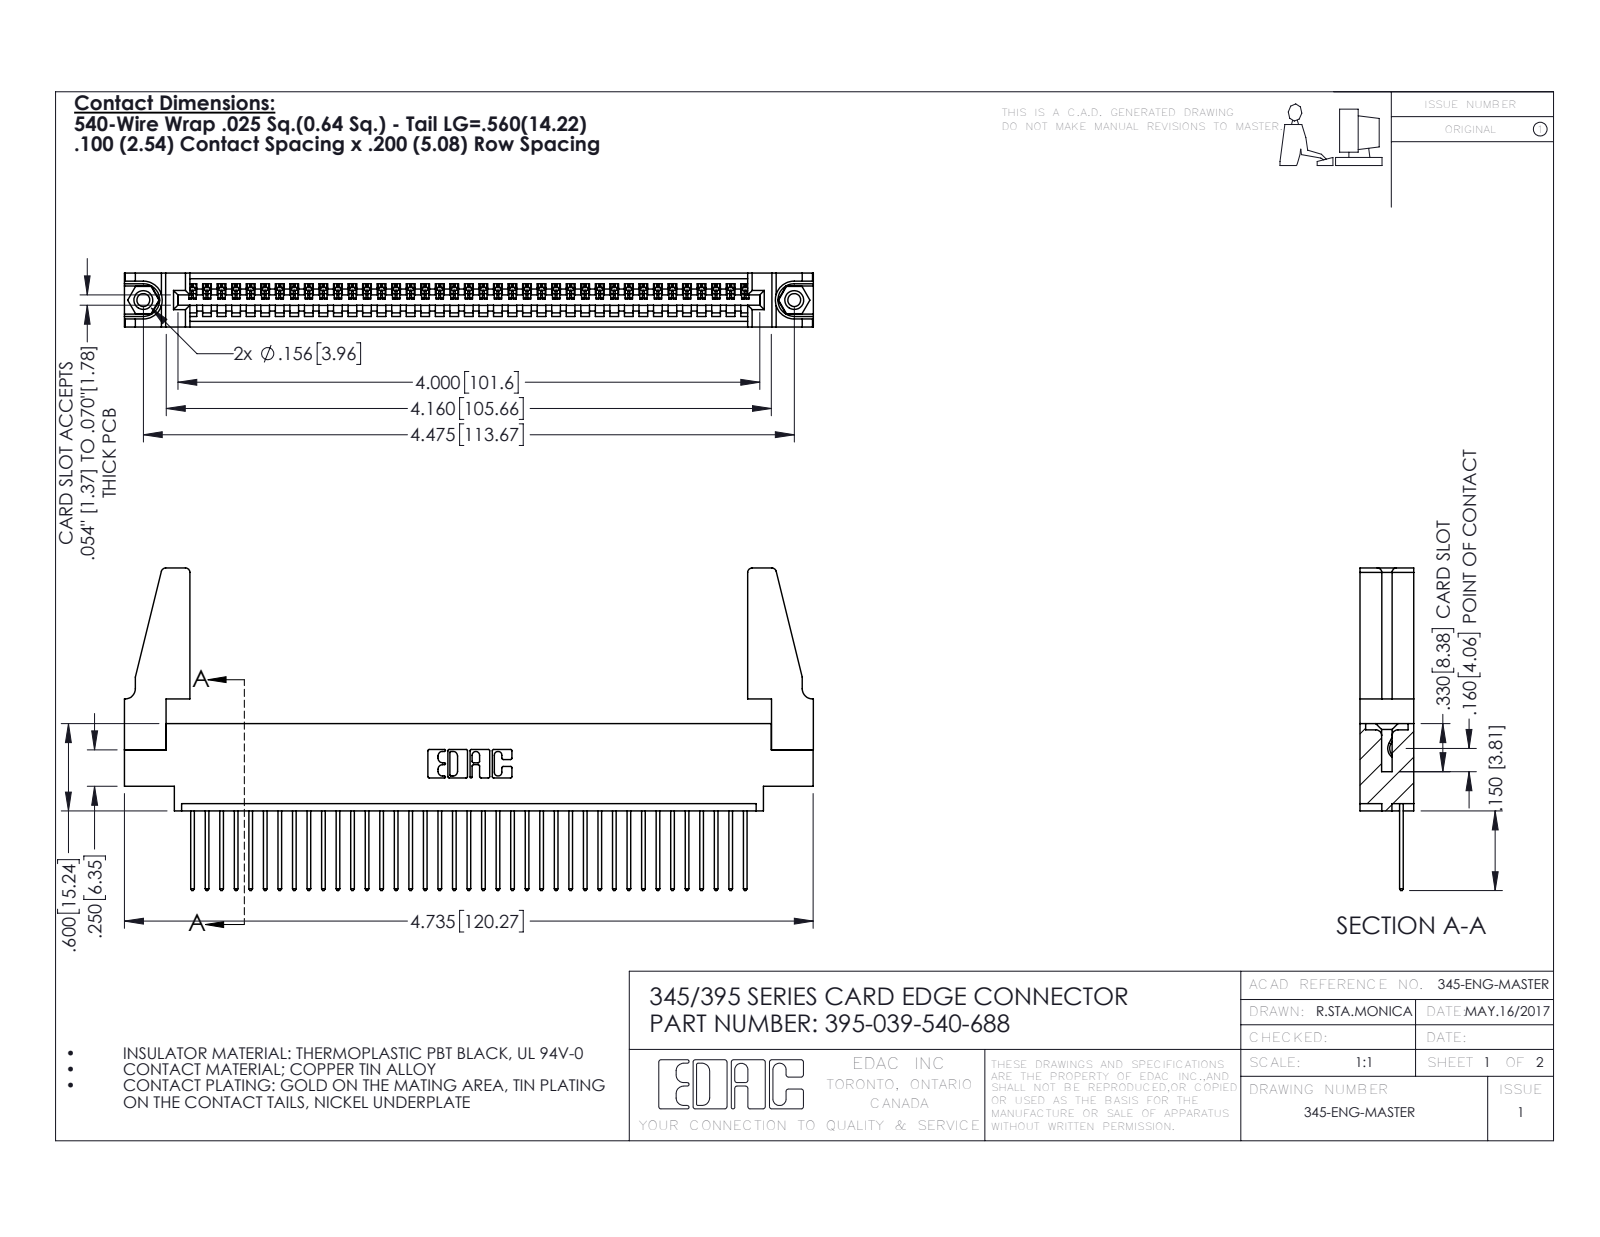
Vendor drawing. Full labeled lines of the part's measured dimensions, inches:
Part name (STEP PRODUCT): 345-250-001_345-250-001-102; 345-292-001_345-293-140; 395-039-540-688; 345 Part_0.170 Offset - 0.156 Dia-TH (+1 more)
STEP written by: SolidWorks 2016 (CONFIG_CONTROL_DESIGN)
Units: inches
Bodies: 44 solids, 2516 faces (1716 planar, 784 cylindrical, 16 other)
Overall size (bounding box): 4.736 × 2.217 × 0.37
Volume: 0.891 in³ · Surface area: 28.93 in²
Round holes (diameter × count): ⌀0.089 ×2, ⌀0.125 ×2, ⌀0.156 ×2, ⌀0.064 ×1
Round bosses / shafts (diameter × count): ⌀0.155 ×2
Partial cylindrical surfaces — rounded edges, fillets, slot ends (radius × count): R0.006 ×78, R0.01 ×78, R0.01 ×22, R0.03 ×8, R0.007 ×6, R0.031 ×6, R0.026 ×3, R0.031 ×2
Main face-to-face distances: 0.072, 0.298, 0.37, 0.098, 0.272, 0.025, 0.2, 0.225, 0.175, 0.149
Hole centre spacings: 0.27, 4.239, 4.475
